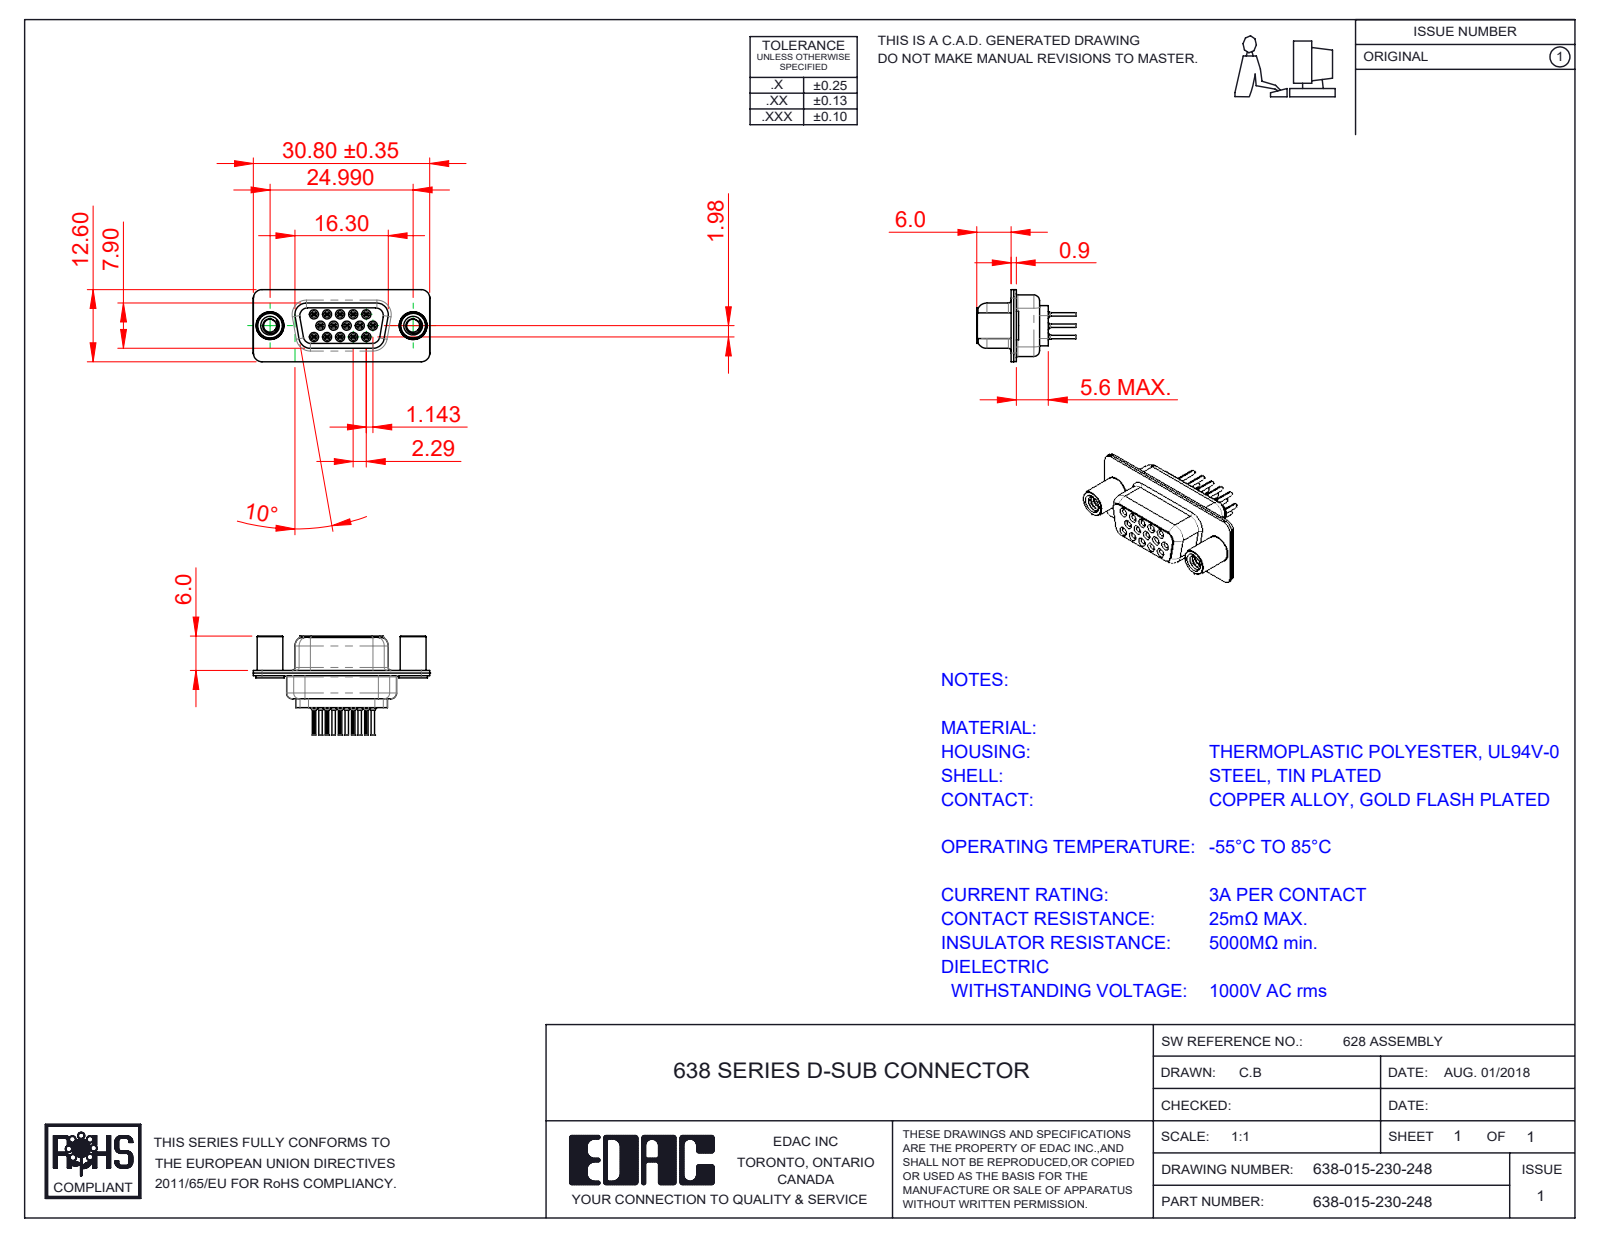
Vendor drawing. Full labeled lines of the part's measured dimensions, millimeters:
Part name (STEP PRODUCT): 638 Housing_15 Contacts; 638-015-230-248; 638 Shell Rear_15 Contacts; 638 Contact Row 2_30 (+4 more)
STEP written by: SolidWorks 2020 (CONFIG_CONTROL_DESIGN)
Units: millimetres
Bodies: 20 solids, 2218 faces (534 planar, 660 cylindrical, 1024 other)
Overall size (bounding box): 30.81 × 17.3 × 12.6
Volume: 1 639 mm³ · Surface area: 5 791 mm²
Round holes (diameter × count): ⌀0.2 ×15, ⌀0.8 ×15, ⌀1 ×15, ⌀1.1 ×15, ⌀1.6 ×15, ⌀1.7 ×15, ⌀1.8 ×15, ⌀2 ×2, ⌀2.26 ×2, ⌀4 ×2, ⌀4.05 ×2, ⌀4.85 ×2
Round bosses / shafts (diameter × count): ⌀2 ×15, ⌀1.5 ×15, ⌀1.2 ×15, ⌀0.6 ×15, ⌀5 ×2, ⌀4.95 ×2, ⌀4.8 ×2, ⌀4.5 ×2
Partial cylindrical surfaces — rounded edges, fillets, slot ends (radius × count): R0.1 ×30, R1.5 ×20, R2 ×12, R0.28 ×10, R1.55 ×8, R1.35 ×5, R0.25 ×4, R0.5 ×4
Main face-to-face distances: 0.45, 0.9, 0.4, 1.43, 8.88, 6.6, 1.4, 0.85, 2.28, 1.8
Hole centre spacings: 3.96, 2.28, 4.57, 2.29, 6.05, 6.04, 6.86, 7.92
